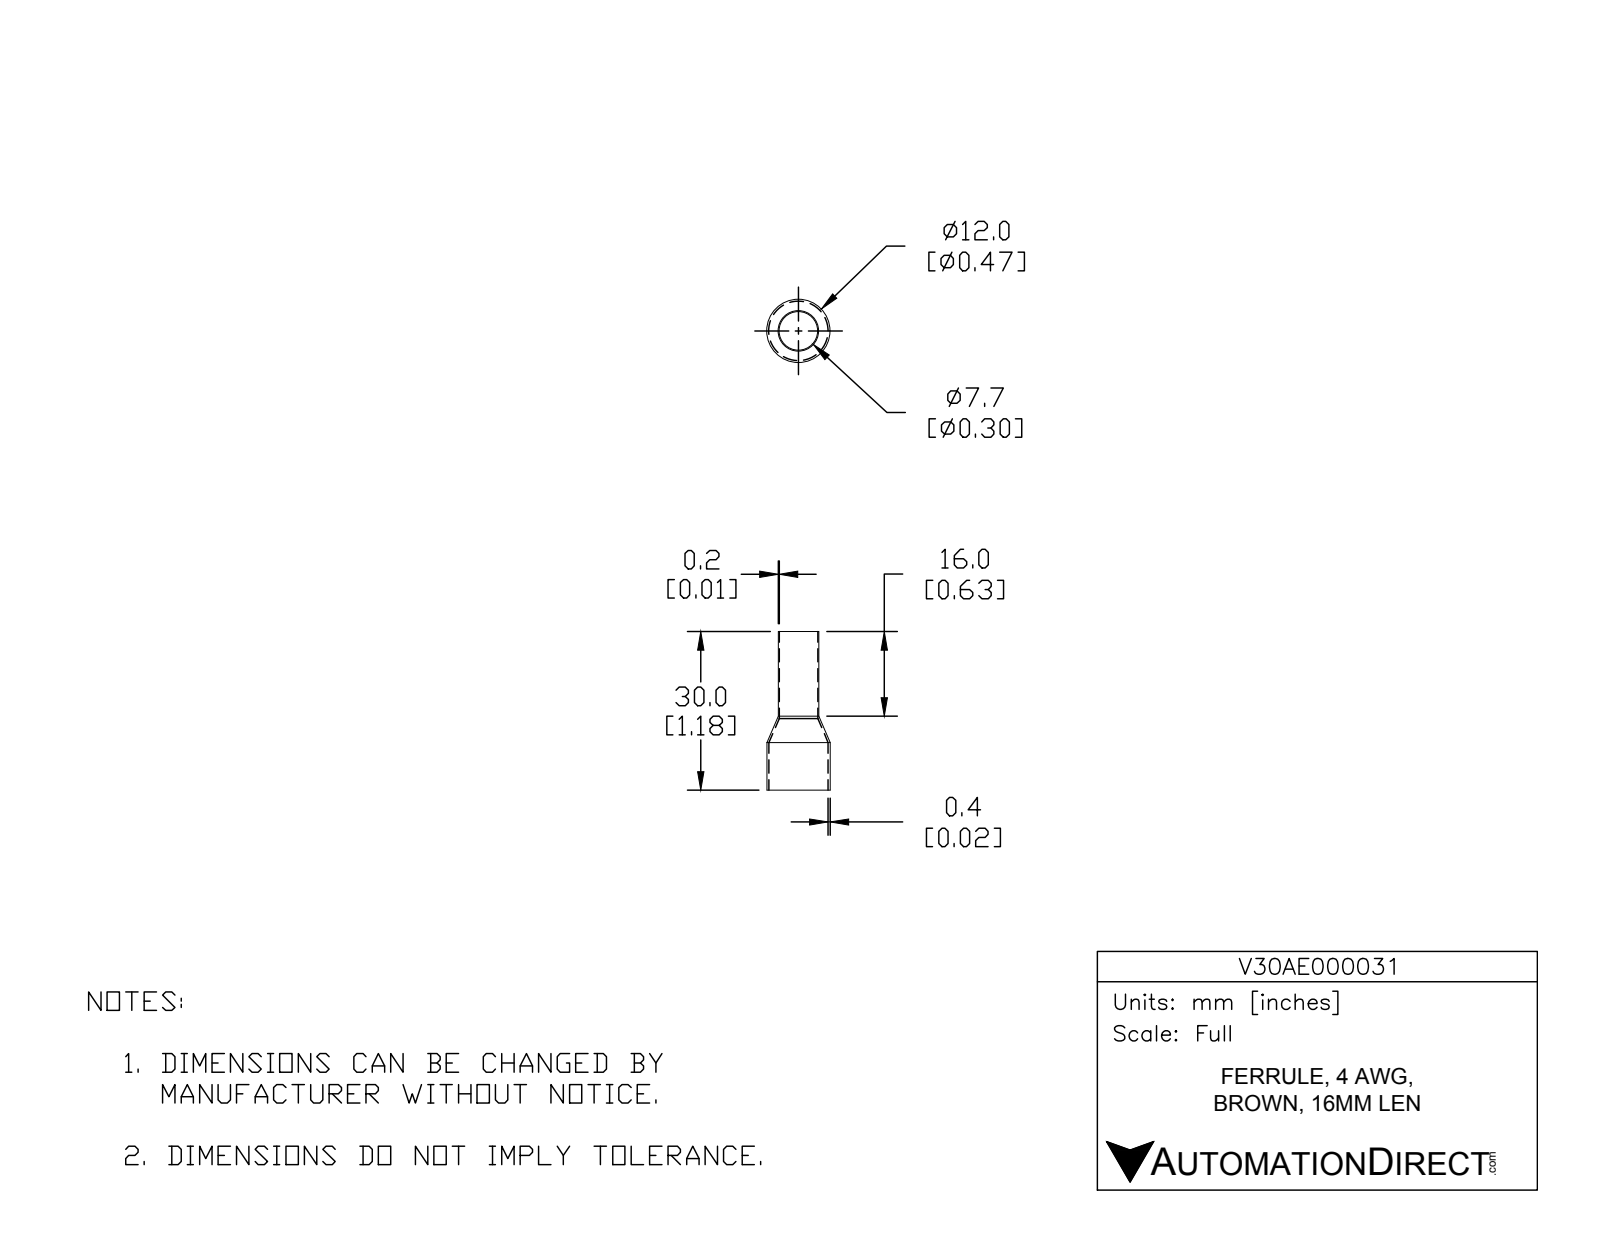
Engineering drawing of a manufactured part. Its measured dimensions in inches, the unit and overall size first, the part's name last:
Units: inches
Overall size (bounding box): 1.181 × 0.472 × 0.472
Round holes (diameter × count): ⌀0.287 ×1, ⌀0.441 ×1
Round bosses / shafts (diameter × count): ⌀0.472 ×1, ⌀0.303 ×1
Main face-to-face distances: 1.181
Volume: 0.016 in³ · Surface area: 2.716 in²
Bodies: 1 solid, 14 faces (2 planar, 8 cylindrical, 4 other)
Part name (STEP PRODUCT): V30AE000031
STEP written by: SolidWorks 2017 (AUTOMOTIVE_DESIGN)
